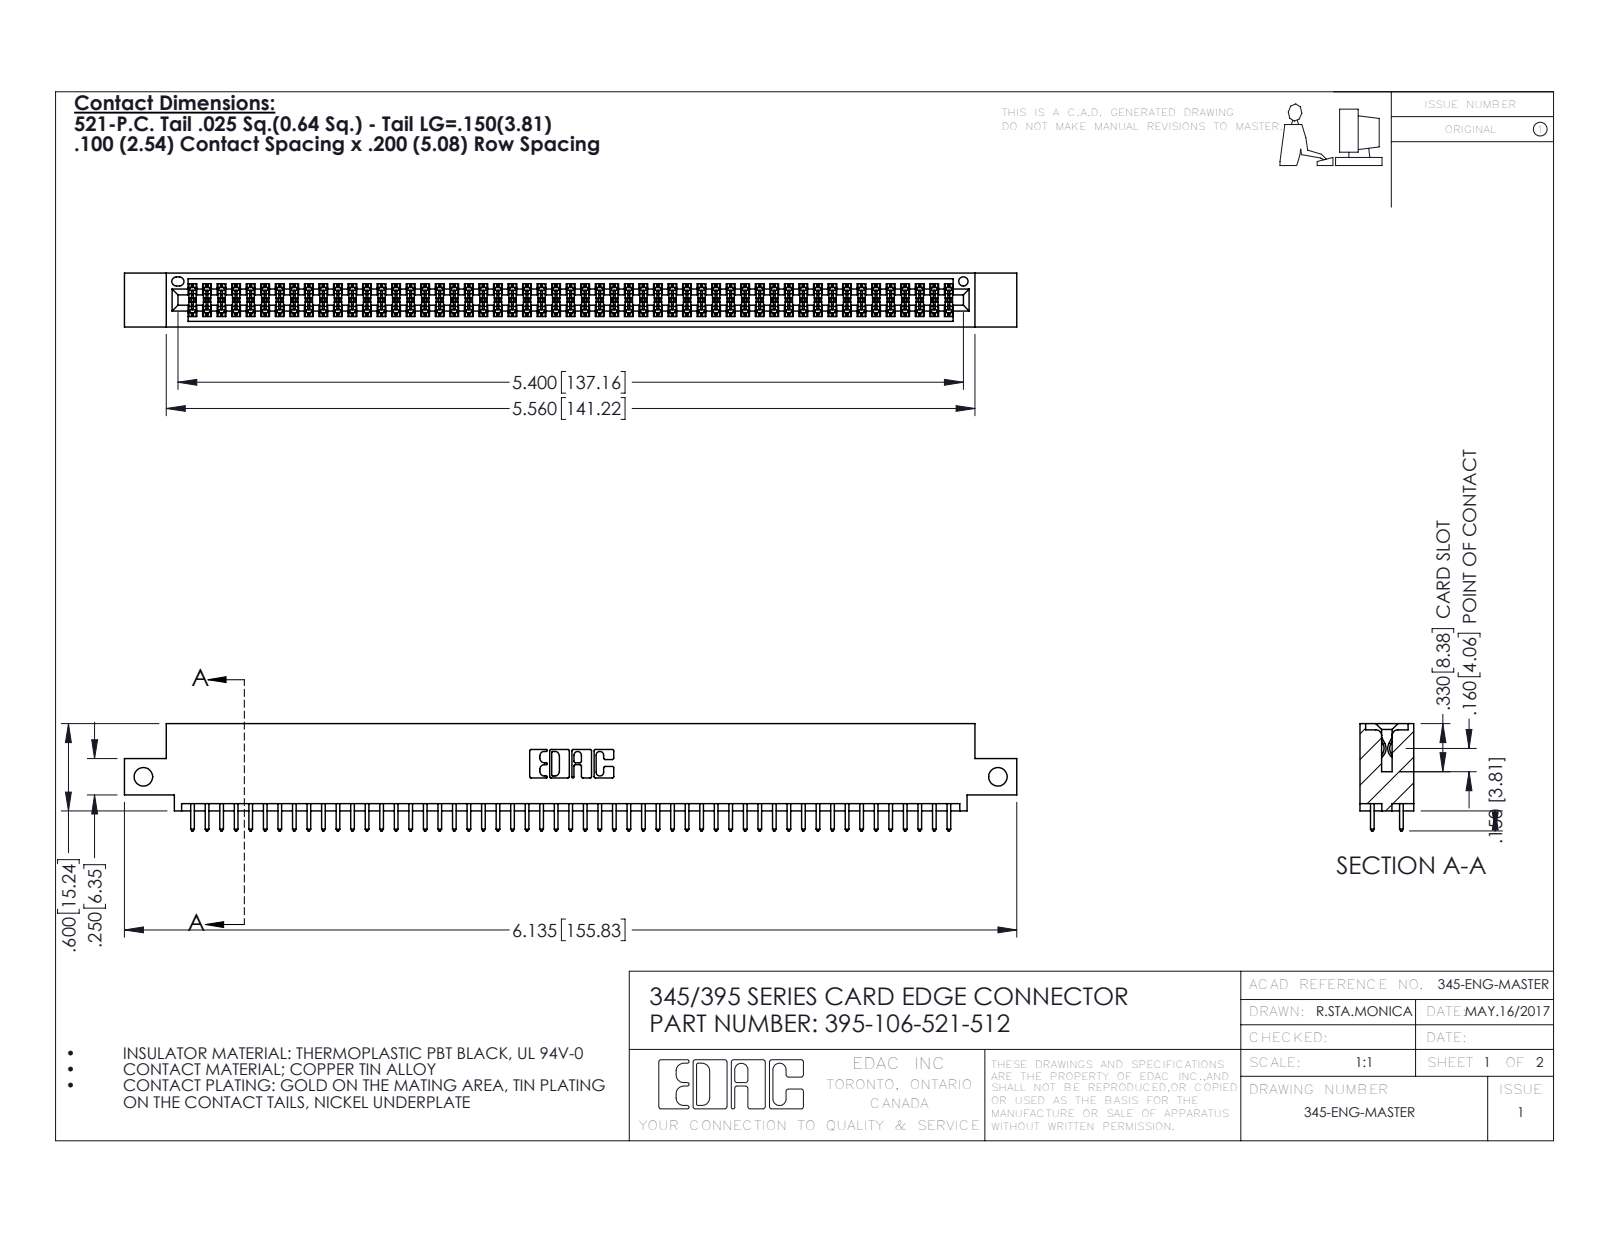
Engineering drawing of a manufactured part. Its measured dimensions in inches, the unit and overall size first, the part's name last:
Units: inches
Overall size (bounding box): 6.135 × 0.737 × 0.37
Round holes (diameter × count): ⌀0.128 ×2, ⌀0.064 ×1
Partial cylindrical surfaces — rounded edges, fillets, slot ends (radius × count): R0.006 ×159, R0.01 ×106, R0.01 ×22, R0.007 ×6, R0.031 ×6, R0.026 ×3, R0.014 ×2, R0.019 ×2
Main face-to-face distances: 0.298, 0.072, 0.2, 0.098, 0.272, 0.025, 0.37, 0.225, 0.175, 0.149
Hole centre spacings: 5.875
Volume: 0.918 in³ · Surface area: 34.28 in²
Bodies: 107 solids, 5430 faces (3582 planar, 1848 cylindrical, 0 other)
Part name (STEP PRODUCT): 395-106-521-512; 345-292-001_345-293-121; 345 Part_0.110 Offset - Side Mount
STEP written by: SolidWorks 2016 (CONFIG_CONTROL_DESIGN)
